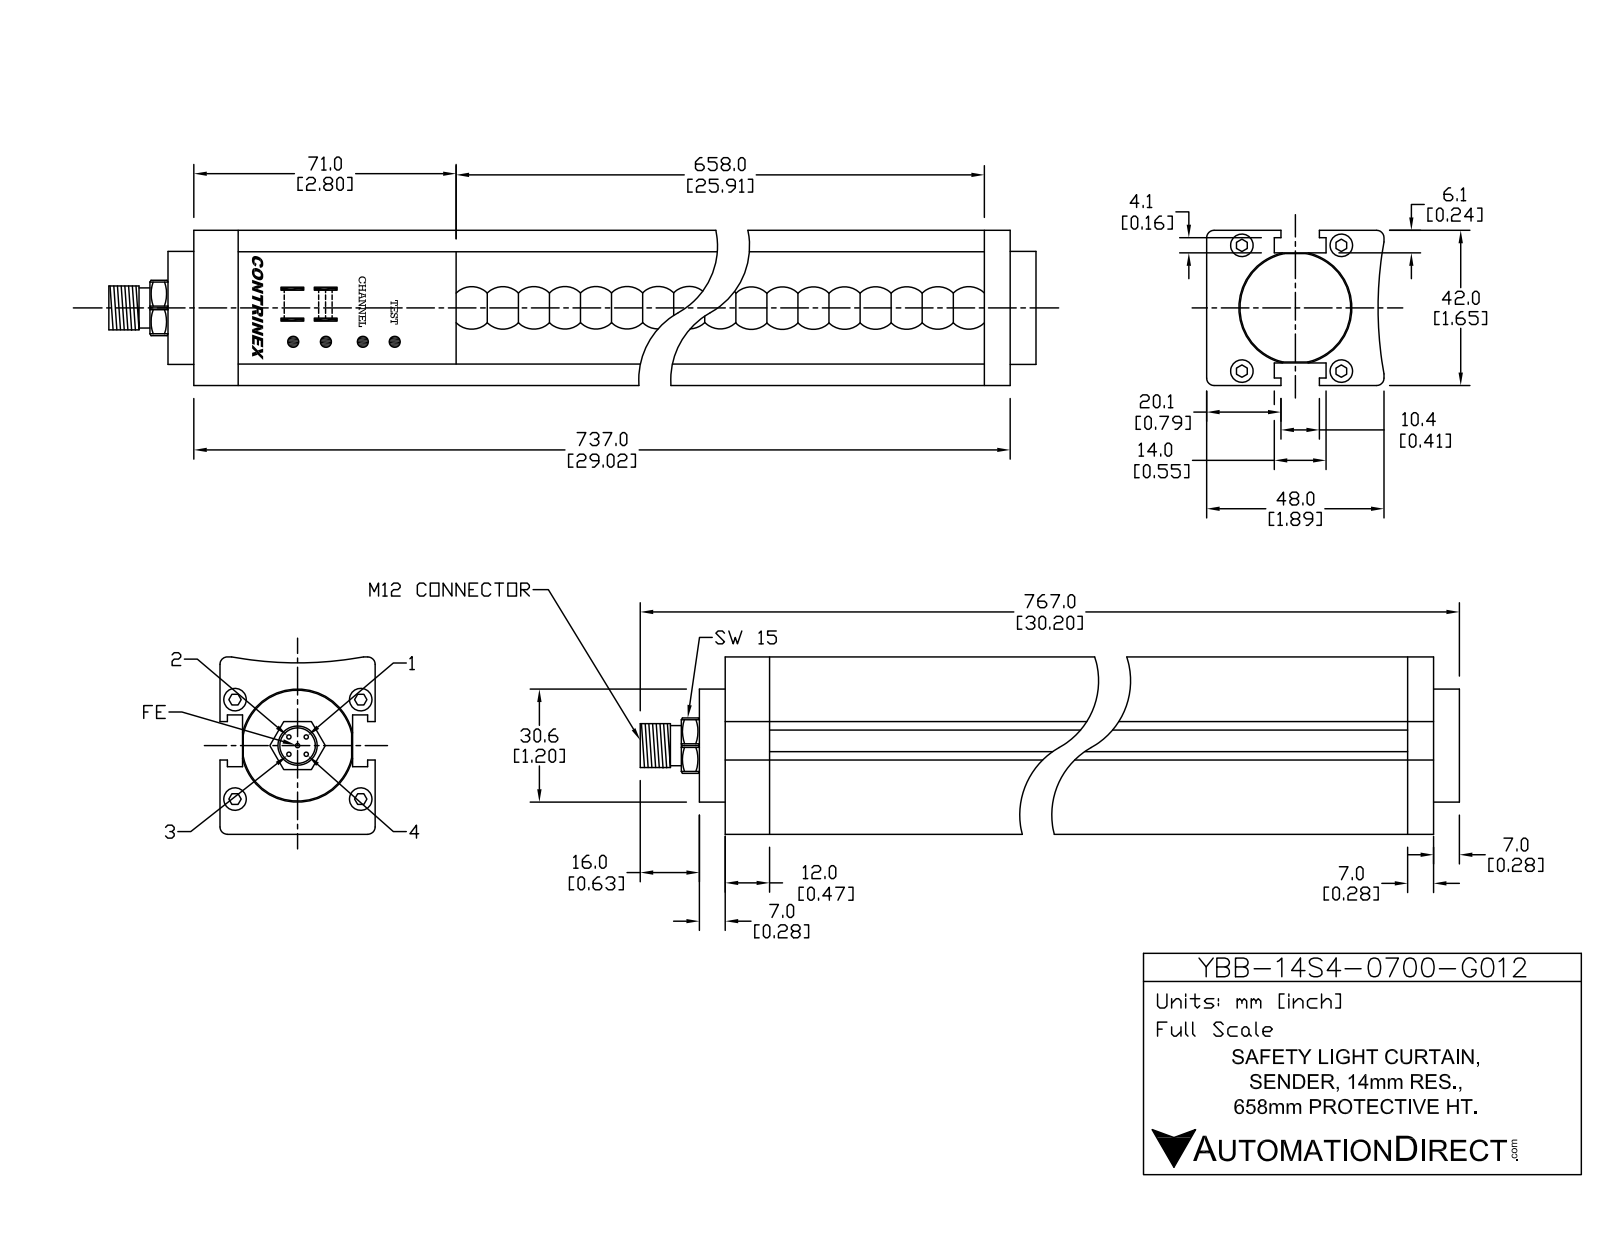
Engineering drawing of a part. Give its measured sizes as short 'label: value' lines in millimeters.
name: YBB-14S4-0700-G012
written by: SolidWorks 2016 (AUTOMOTIVE_DESIGN)
unit: mm
bodies: 19 solids, 440 faces (208 planar, 168 cylindrical, 64 other)
size: 767 × 48 × 42
volume: 1 330 000 mm³; area: 174 916 mm²
holes: 4× ⌀6, 1× ⌀8.5, 1× ⌀32
bosses: 5× ⌀1, 4× ⌀5.5, 1× ⌀30.6, 1× ⌀12, 1× ⌀10.5
rounds: 48× R1, 4× R0.5, 2× R0.55, 1× R8.2, 1× R100
face distances: 6.3, 35.7, 42, 29.4, 14, 17.2, 31.2, 15.7, 29.7, 46.9
hole spacings: 21.04, 22.34, 26.9, 34, 43.35
